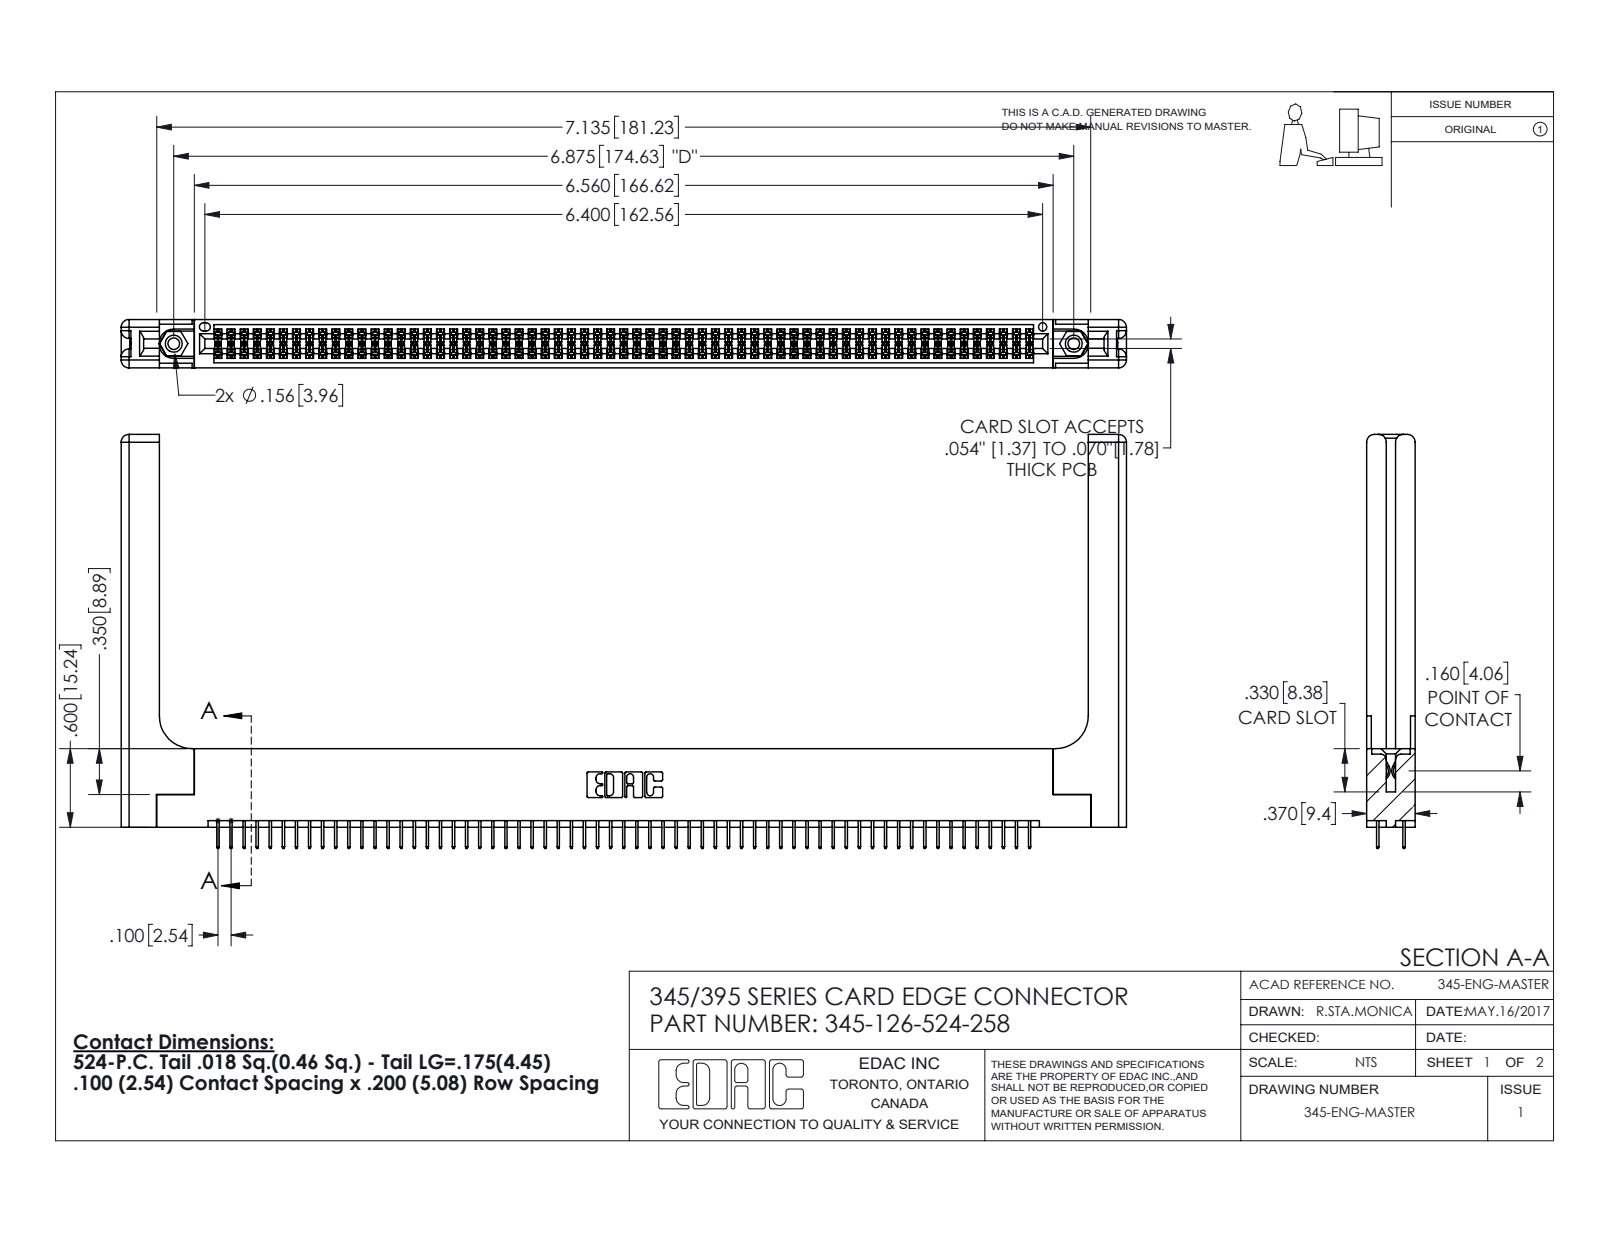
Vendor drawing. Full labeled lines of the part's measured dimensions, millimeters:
Part name (STEP PRODUCT): 345-220-058_345-220-058; 345-250-001_345-250-001-102; 345-292-001_345-293-124; 345 Part_Flush Mounting Lugs - 0.156 Dia-TH (+1 more)
STEP written by: SolidWorks 2016 (CONFIG_CONTROL_DESIGN)
Units: millimetres
Bodies: 131 solids, 7186 faces (5142 planar, 1984 cylindrical, 60 other)
Overall size (bounding box): 195 × 80.3 × 9.4
Volume: 27 430 mm³ · Surface area: 32 970 mm²
Round holes (diameter × count): ⌀2.3 ×2, ⌀3.2 ×2, ⌀4 ×2, ⌀1.6 ×1
Round bosses / shafts (diameter × count): ⌀3.9 ×2
Partial cylindrical surfaces — rounded edges, fillets, slot ends (radius × count): R0.2 ×189, R0.3 ×22, R1.5 ×16, R0.2 ×6, R0.8 ×6, R0.7 ×3, R0.4 ×2, R0.5 ×2
Main face-to-face distances: 1.8, 7.6, 9.4, 5.1, 2.5, 6.9, 0.6, 5.7, 1.8, 3.8
Hole centre spacings: 6.9, 168.6, 174.6
